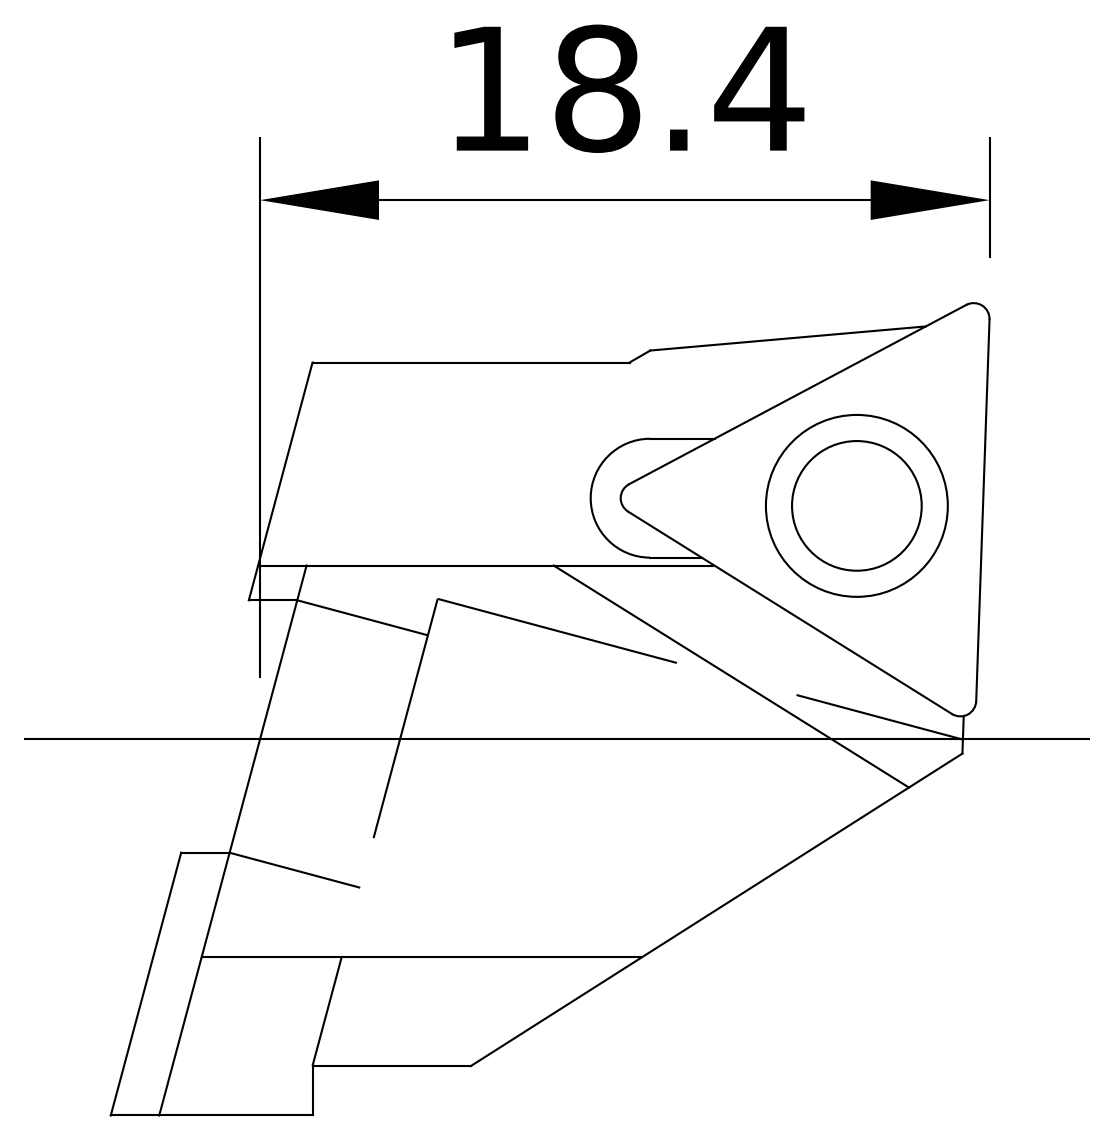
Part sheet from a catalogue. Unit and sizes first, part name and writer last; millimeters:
Units: millimetres
Overall size (bounding box): 22.12 × 21.3 × 13
Round holes (diameter × count): ⌀2.01 ×1, ⌀2.8 ×1
Round bosses / shafts (diameter × count): ⌀3.45 ×1, ⌀2.5 ×1
Partial cylindrical surfaces — rounded edges, fillets, slot ends (radius × count): R0.15 ×6, R0.4 ×6, R2.6 ×2, R1.6 ×1, R4.4 ×1, R9.2 ×1, R10.2 ×1
Main face-to-face distances: 13, 6.5, 2.1, 10.9, 4.4, 4.8, 8.2, 4.01, 1.7, 6.1
Volume: 1 961 mm³ · Surface area: 1 878 mm²
Bodies: 3 solids, 102 faces (37 planar, 38 cylindrical, 27 other)
Part name (STEP PRODUCT): 615.302 Kaiser E22_27 TC11|694.122 Kaiser ETL M2.5x6.5 T7 IP 10S;Kreismuster1; 615.302 Kaiser E22_27 TC11|655.383 Kaiser TCGT 110204 K10C;Kombinieren1; 615.302 Kaiser E22_27 TC11|615.302 Kaiser E22_27 TC11;Verrundung2
STEP written by: ACIS (automotive_design)
